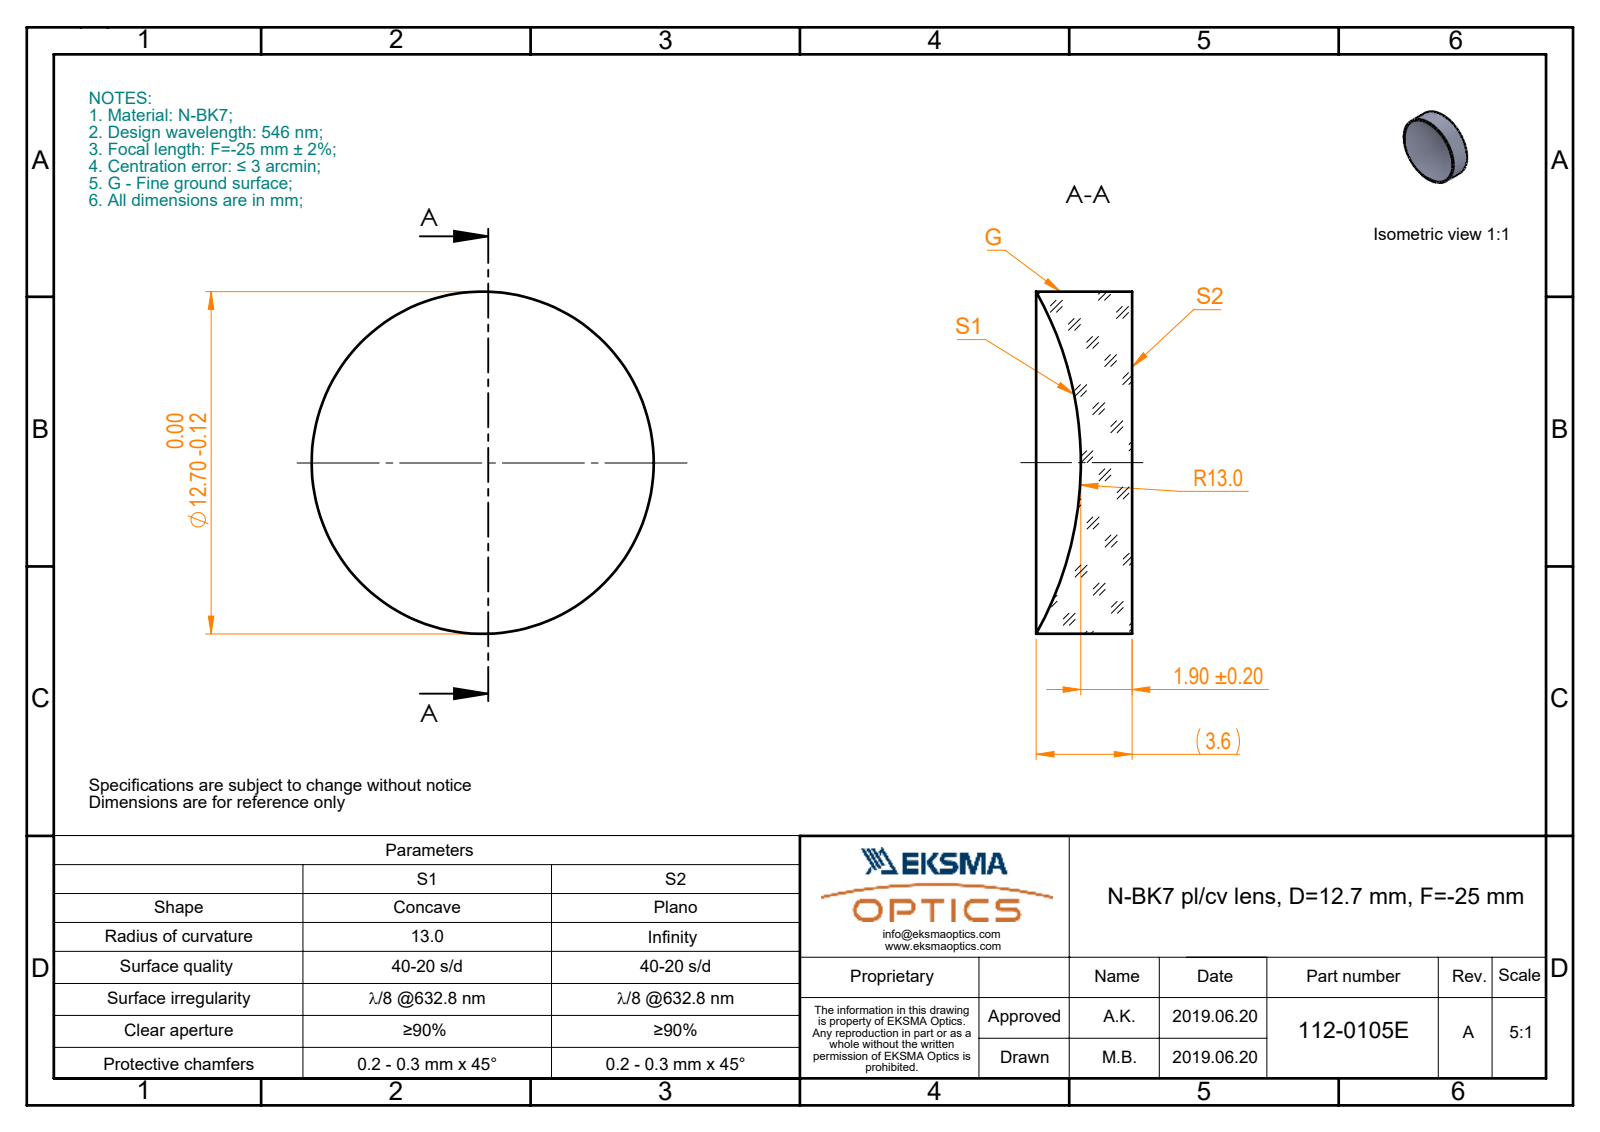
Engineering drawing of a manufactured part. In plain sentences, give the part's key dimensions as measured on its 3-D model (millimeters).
The part is named "112-0105E BK7 pl-cv 12.7 F-12.7". Its 3-D file was written by "SolidWorks 2017 (CONFIG_CONTROL_DESIGN)". It is 1 solid with 5 faces: 1 planar, 2 cylindrical and 2 other. Overall it measures 12.7 by 12.7 by 3.56 millimeters. Its volume is 343 cubic millimeters and its surface area 404 square millimeters. Round bosses or shafts: 1 of diameter 12.7.
